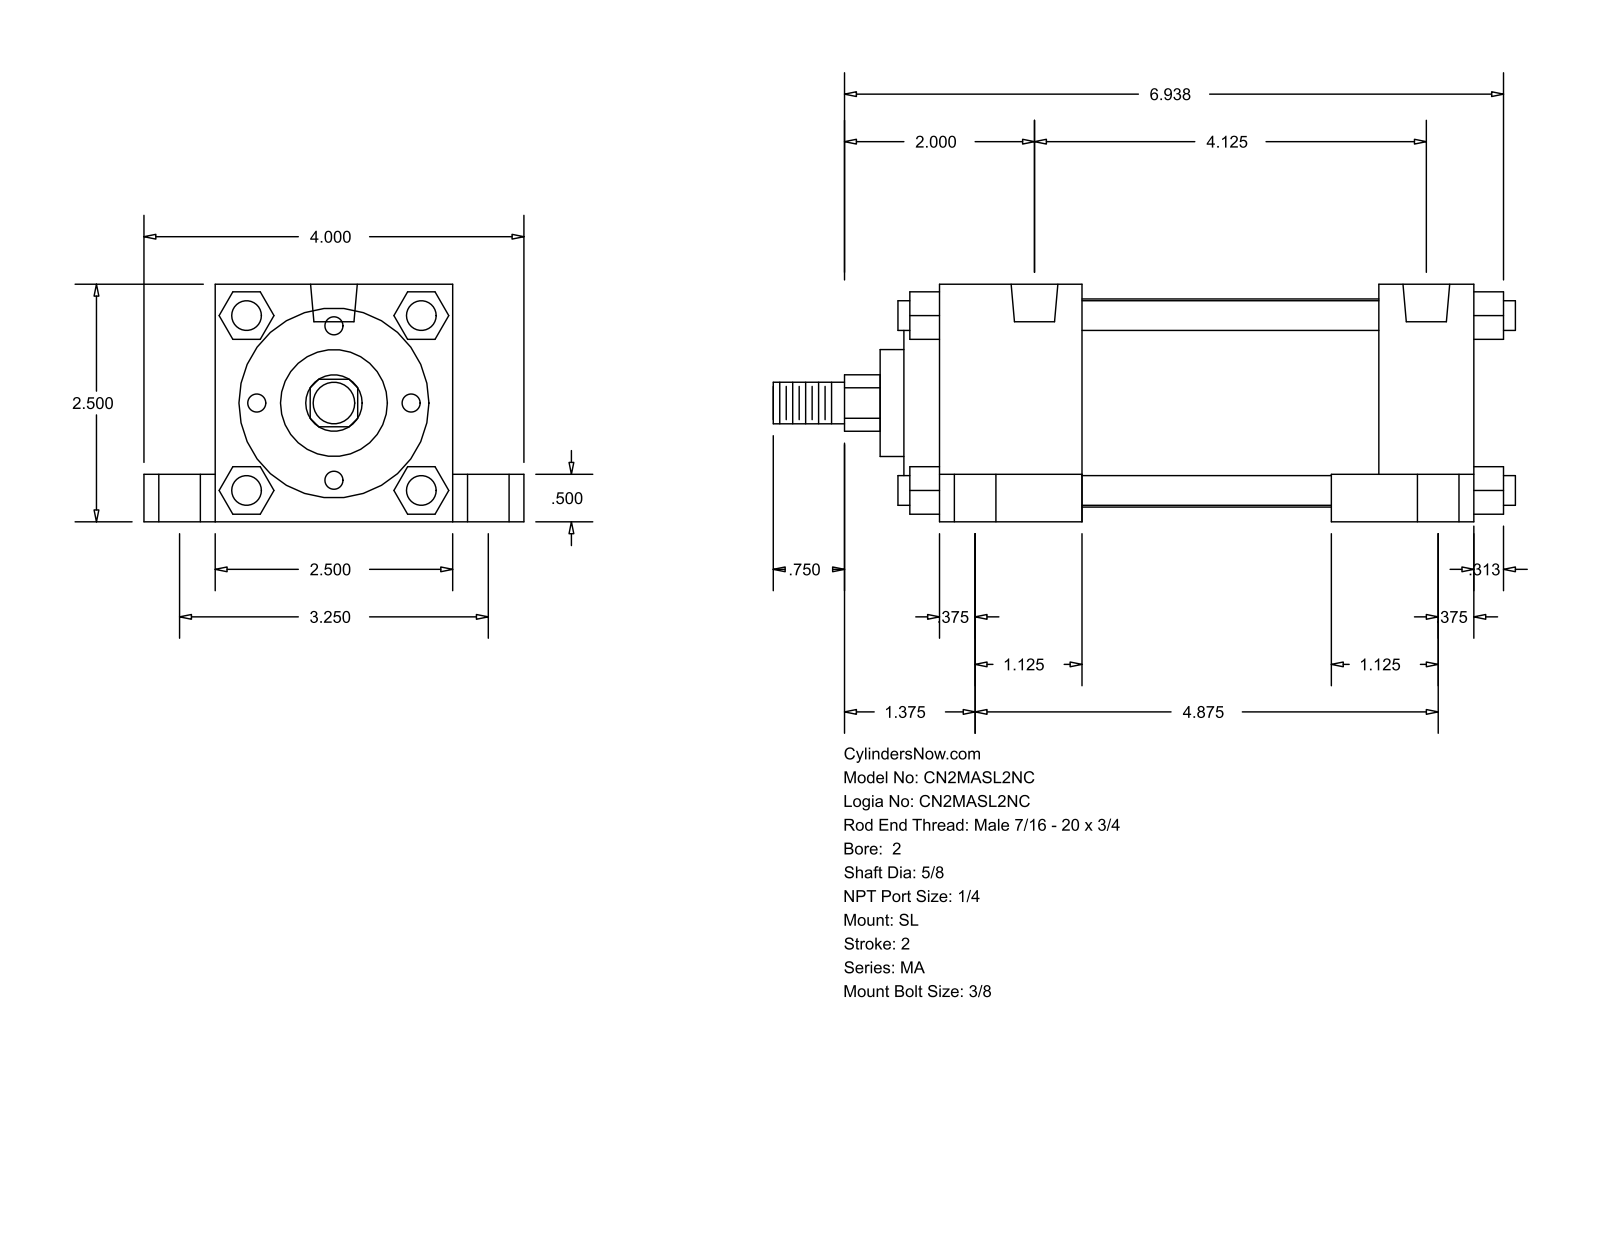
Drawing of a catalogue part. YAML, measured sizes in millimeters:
part_name: "MA_SL__0200_0.625"
step_written_by: "GSSL Pune (CONFIG_CONTROL_DESIGN)"
units: millimeters
bodies: {solids: 0, faces: 150, planar: 113, cylindrical: 37, other: 0}
overall_size: [198.44, 101.6, 63.5]
round_holes:
  - {diameter: 7.94, count: 4}
  - {diameter: 11.11, count: 4}
  - {diameter: 17.46, count: 4}
  - {diameter: 12.49, count: 2}
round_bosses_or_shafts:
  - {diameter: 7.94, count: 4}
  - {diameter: 55.63, count: 1}
  - {diameter: 50.8, count: 1}
  - {diameter: 28.57, count: 1}
  - {diameter: 15.88, count: 1}
  - {diameter: 11.11, count: 1}
partial_cylinders:
  - {radius: 7.54, count: 1}
face_to_face_distances: [63.5, 12.7, 9.52, 25.4, 19.05, 82.55, 38.1, 142.88, 50.8, 104.78]
hole_center_spacings: [41.39, 44.22, 82.54, 104.77, 115.57, 123.83, 127.51, 148.82]
